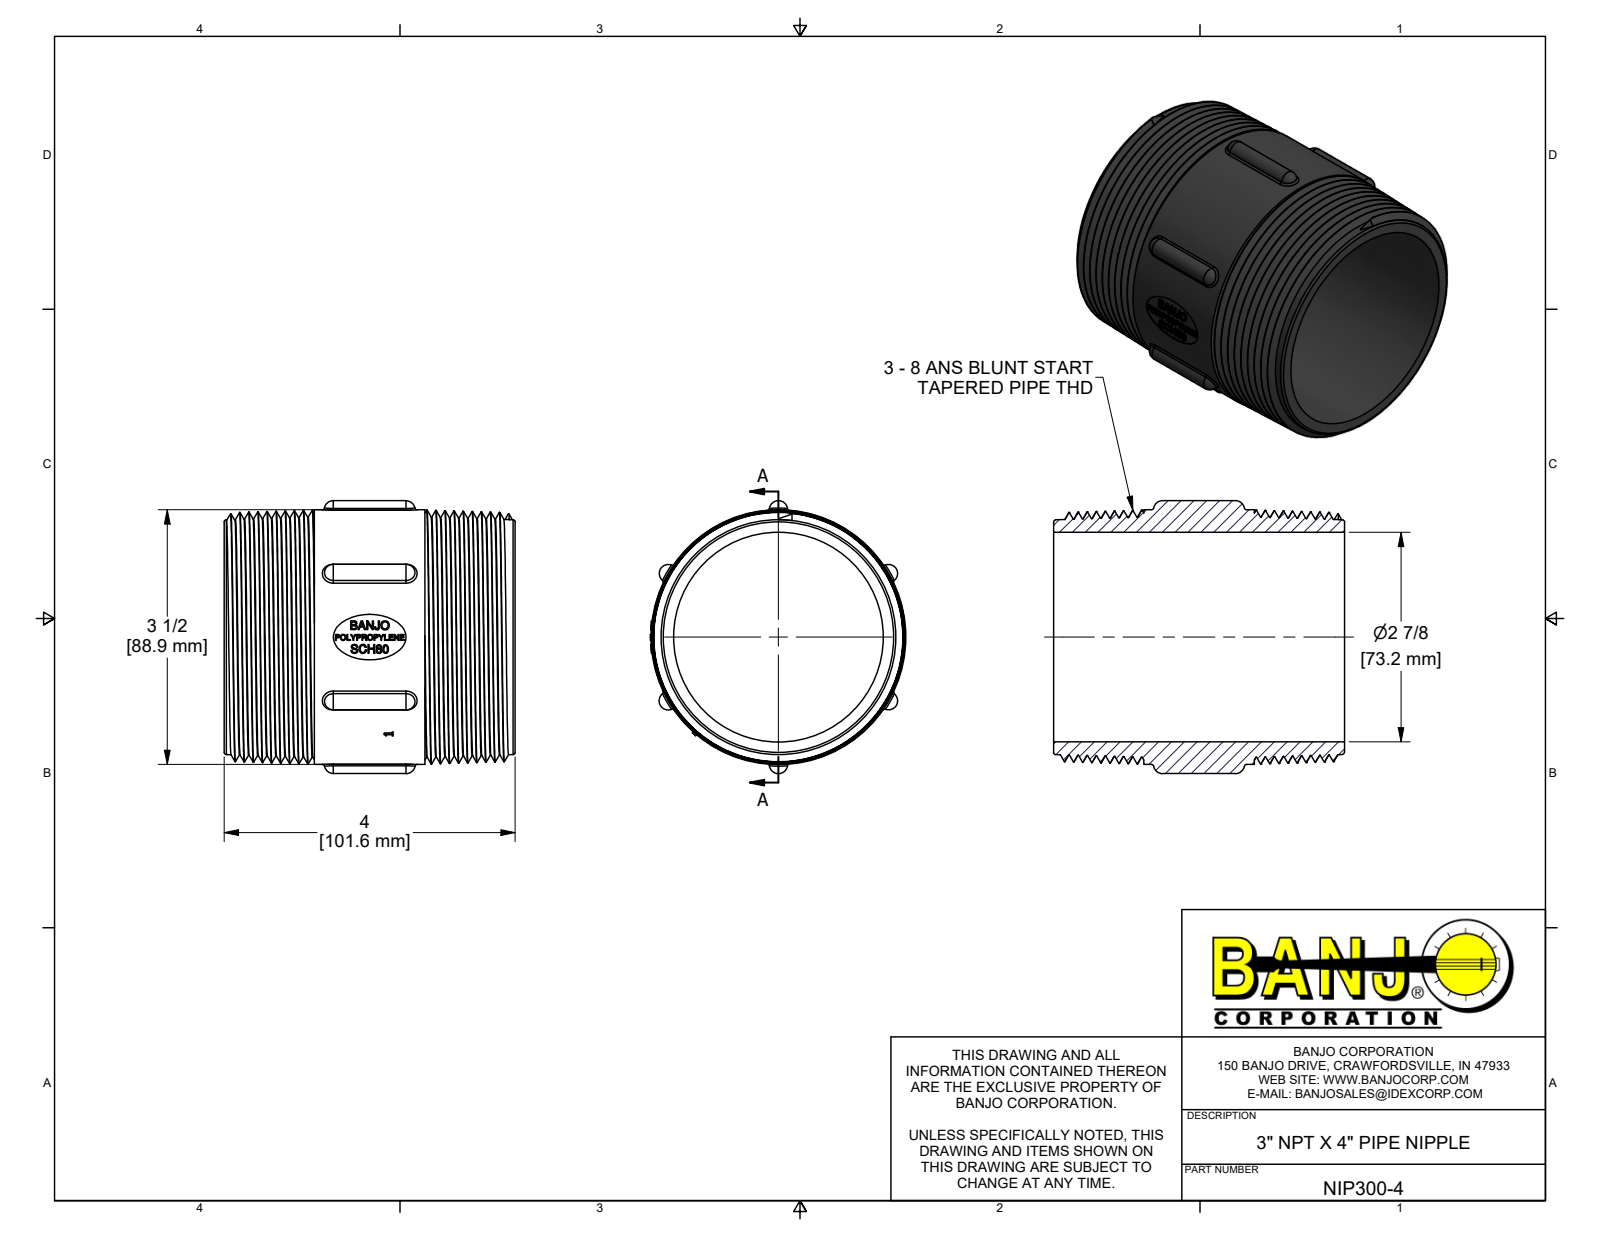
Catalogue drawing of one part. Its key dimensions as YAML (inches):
part_name: "NIP300-4; NIP300-4U"
step_written_by: "Autodesk Inventor 2019 (AUTOMOTIVE_DESIGN)"
units: inches
bodies: {solids: 1, faces: 423, planar: 168, cylindrical: 58, other: 197}
overall_size: [107.775, 3.75, 3.51]
volume: 10.61
surface_area: 1197
round_holes:
  - {diameter: 2.88, count: 1}
round_bosses_or_shafts:
  - {diameter: 3.5, count: 1}
partial_cylinders:
  - {radius: 0.03, count: 12}
  - {radius: 0.125, count: 6}
  - {radius: 1.74, count: 1}
  - {radius: 1.76, count: 1}
  - {radius: 1.77, count: 1}
face_to_face_distances: [4, 1.24, 2.76, 1.52, 0.015, 0.071, 0.08, 0.035, 0.157, 0.074]
